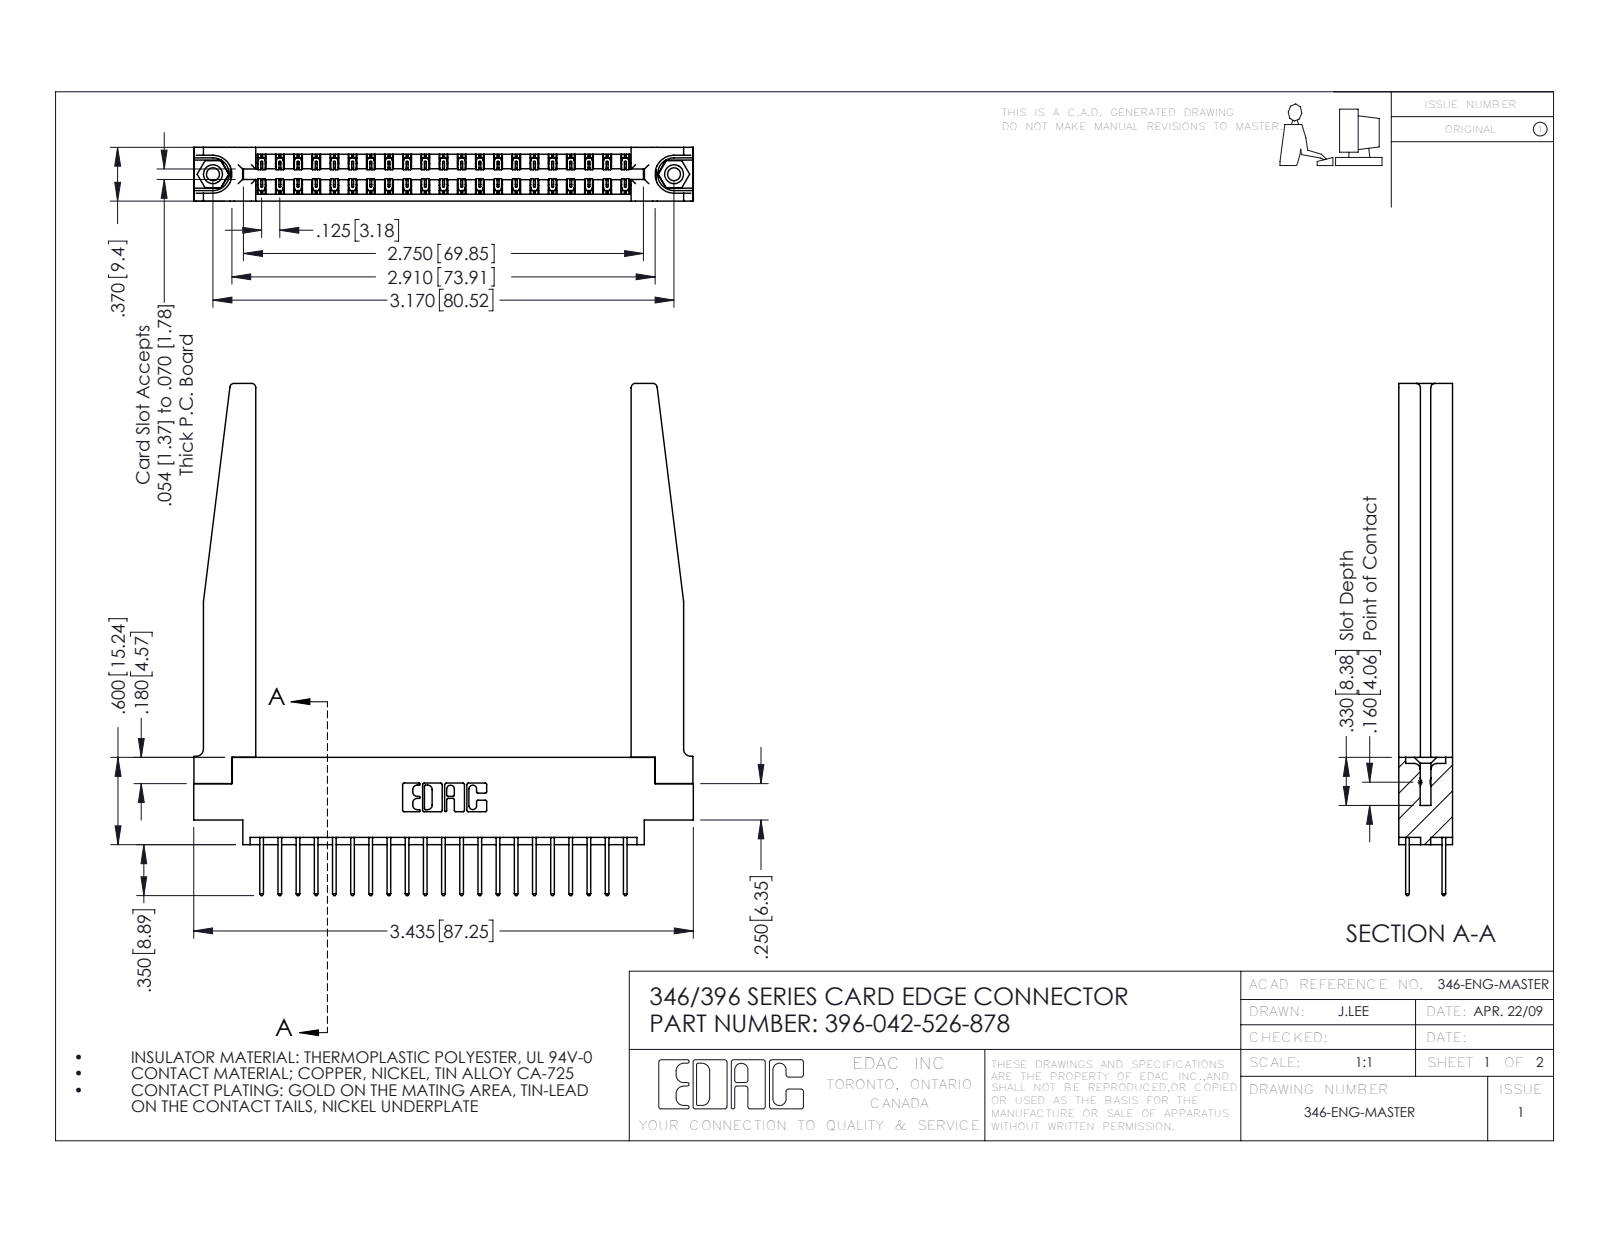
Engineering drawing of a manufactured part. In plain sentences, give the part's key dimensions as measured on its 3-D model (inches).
The part is named "346 Part_0.170 Offset - 0.156 Dia-TH; 346-220-078_345-220-078; 345-250-001_345-250-001-102; 345-292-001_345-293-126 (+1 more)". Its 3-D file was written by "SolidWorks 2016 (CONFIG_CONTROL_DESIGN)". It is 47 solids with 2544 faces: 1692 planar, 800 cylindrical and 52 other. Overall it measures 3.52 by 3.435 by 0.37 inches. Its volume is 0.926 cubic inches and its surface area 27.97 square inches. Round holes: 2 of diameter 0.089, 2 of diameter 0.125, 2 of diameter 0.156, 1 of diameter 0.064. Round bosses or shafts: 2 of diameter 0.155. Partial cylindrical surfaces (rounded edges, fillets, slot ends): 63 of radius 0.006, 42 of radius 0.01, 22 of radius 0.01, 8 of radius 0.03, 6 of radius 0.007, 6 of radius 0.031, 3 of radius 0.026, 2 of radius 0.014. The main face-to-face distances are 0.37, 0.048, 0.322, 0.072, 0.148, 0.15, 0.25, 0.298, 0.025, 0.275. The hole center spacings are 0.246, 2.963, 3.17.
